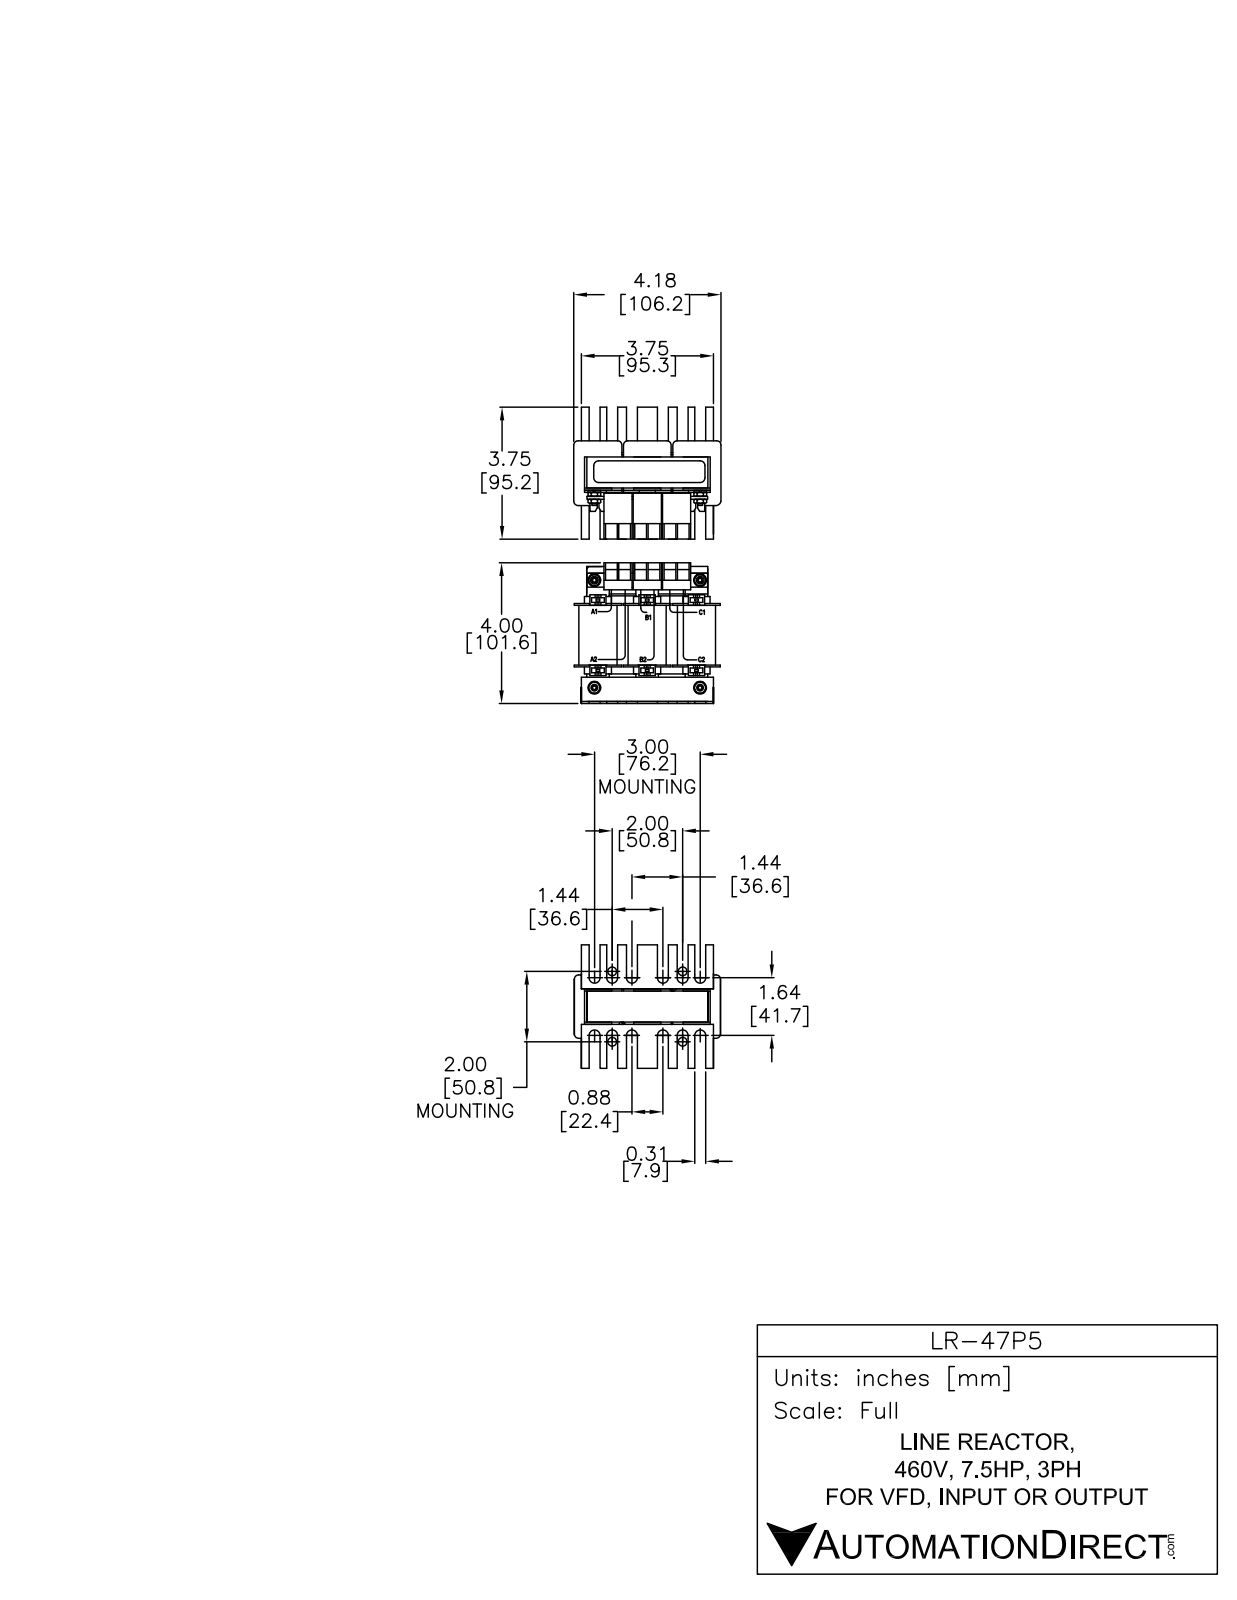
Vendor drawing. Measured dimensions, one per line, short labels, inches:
name: LR-47P5
written by: SolidWorks 2011 (AUTOMOTIVE_DESIGN)
unit: in
bodies: 17 solids, 941 faces (743 planar, 198 cylindrical, 0 other)
size: 4.144 × 3.874 × 3.514
volume: 16.62 in³; area: 153.8 in²
bosses: 4× ⌀0.305, 4× ⌀0.138
rounds: 50× R0.157, 24× R0.072, 12× R0.315, 6× R0.118, 3× R0.034, 2× R0.049
face distances: 0.197, 0.846, 0.108, 2.008, 1.033, 1.043, 0.295, 1.142, 2.795, 0.098
